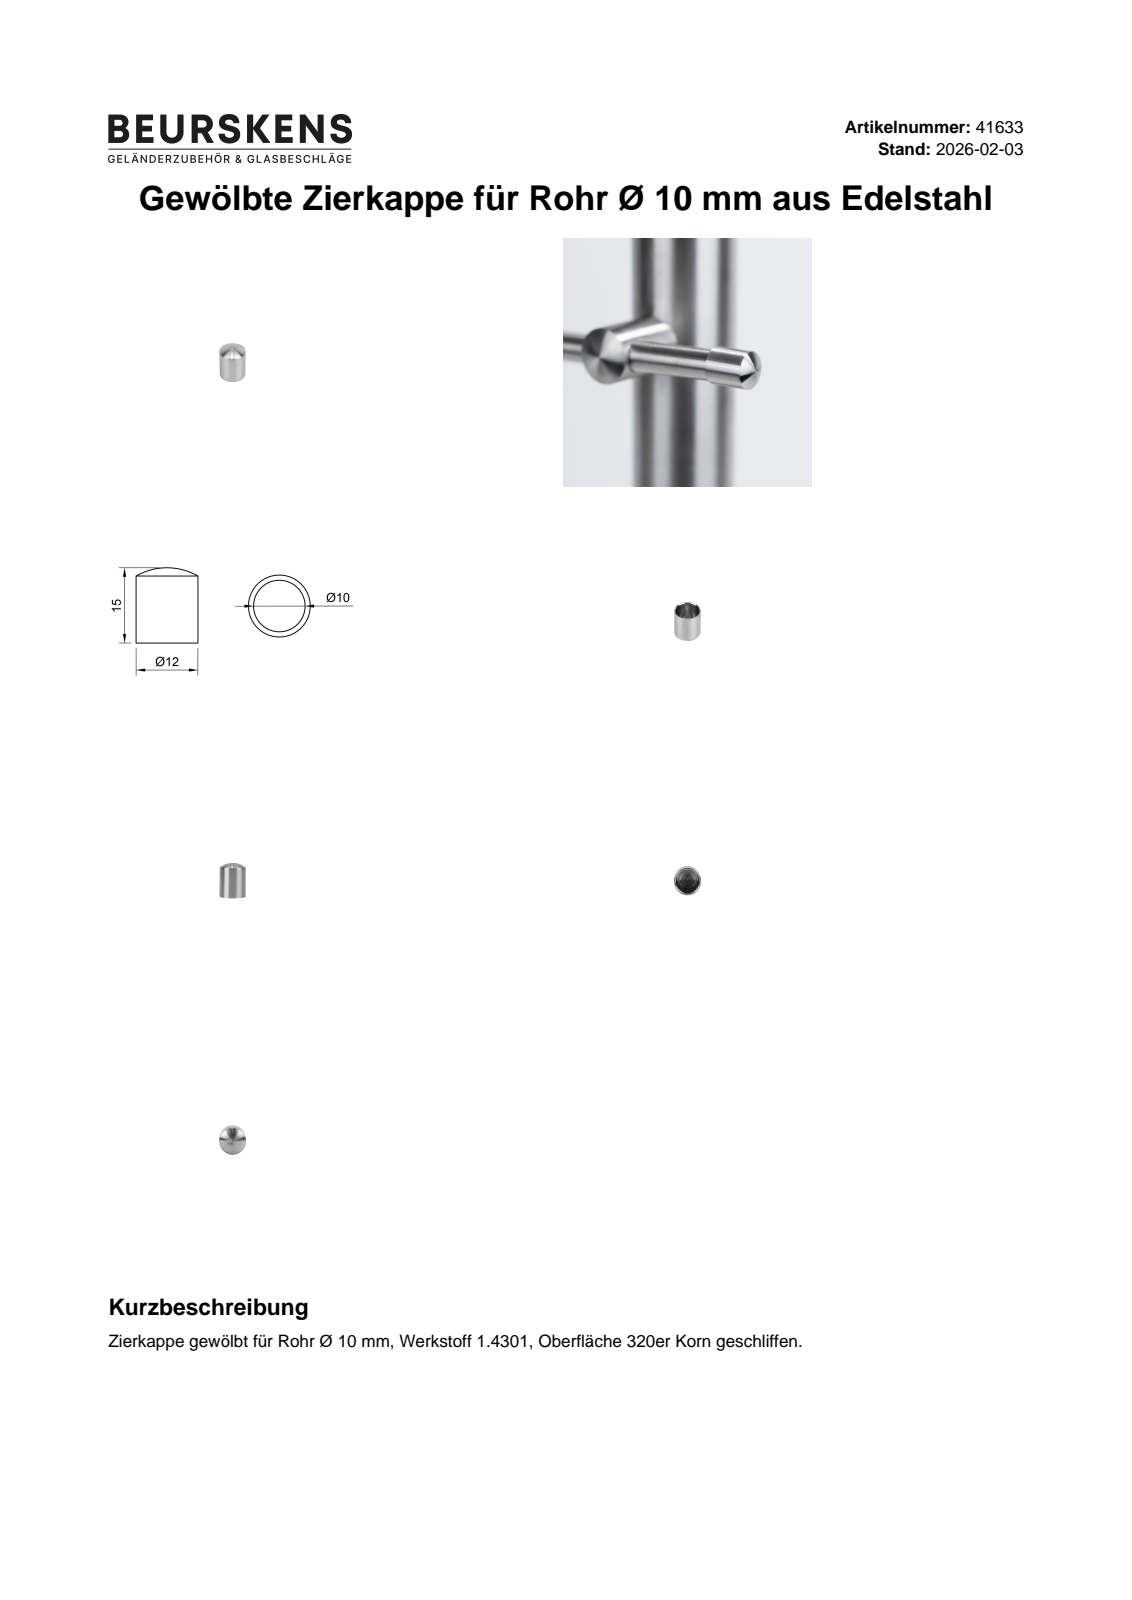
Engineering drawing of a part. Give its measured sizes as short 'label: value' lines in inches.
name: 41633
written by: Autodesk Inventor 2022 (AUTOMOTIVE_DESIGN)
unit: in
bodies: 1 solid, 5 faces (1 planar, 2 cylindrical, 2 other)
size: 0.575 × 0.472 × 0.472
volume: 0.043 in³; area: 1.631 in²
holes: 1× ⌀0.394
bosses: 1× ⌀0.472
